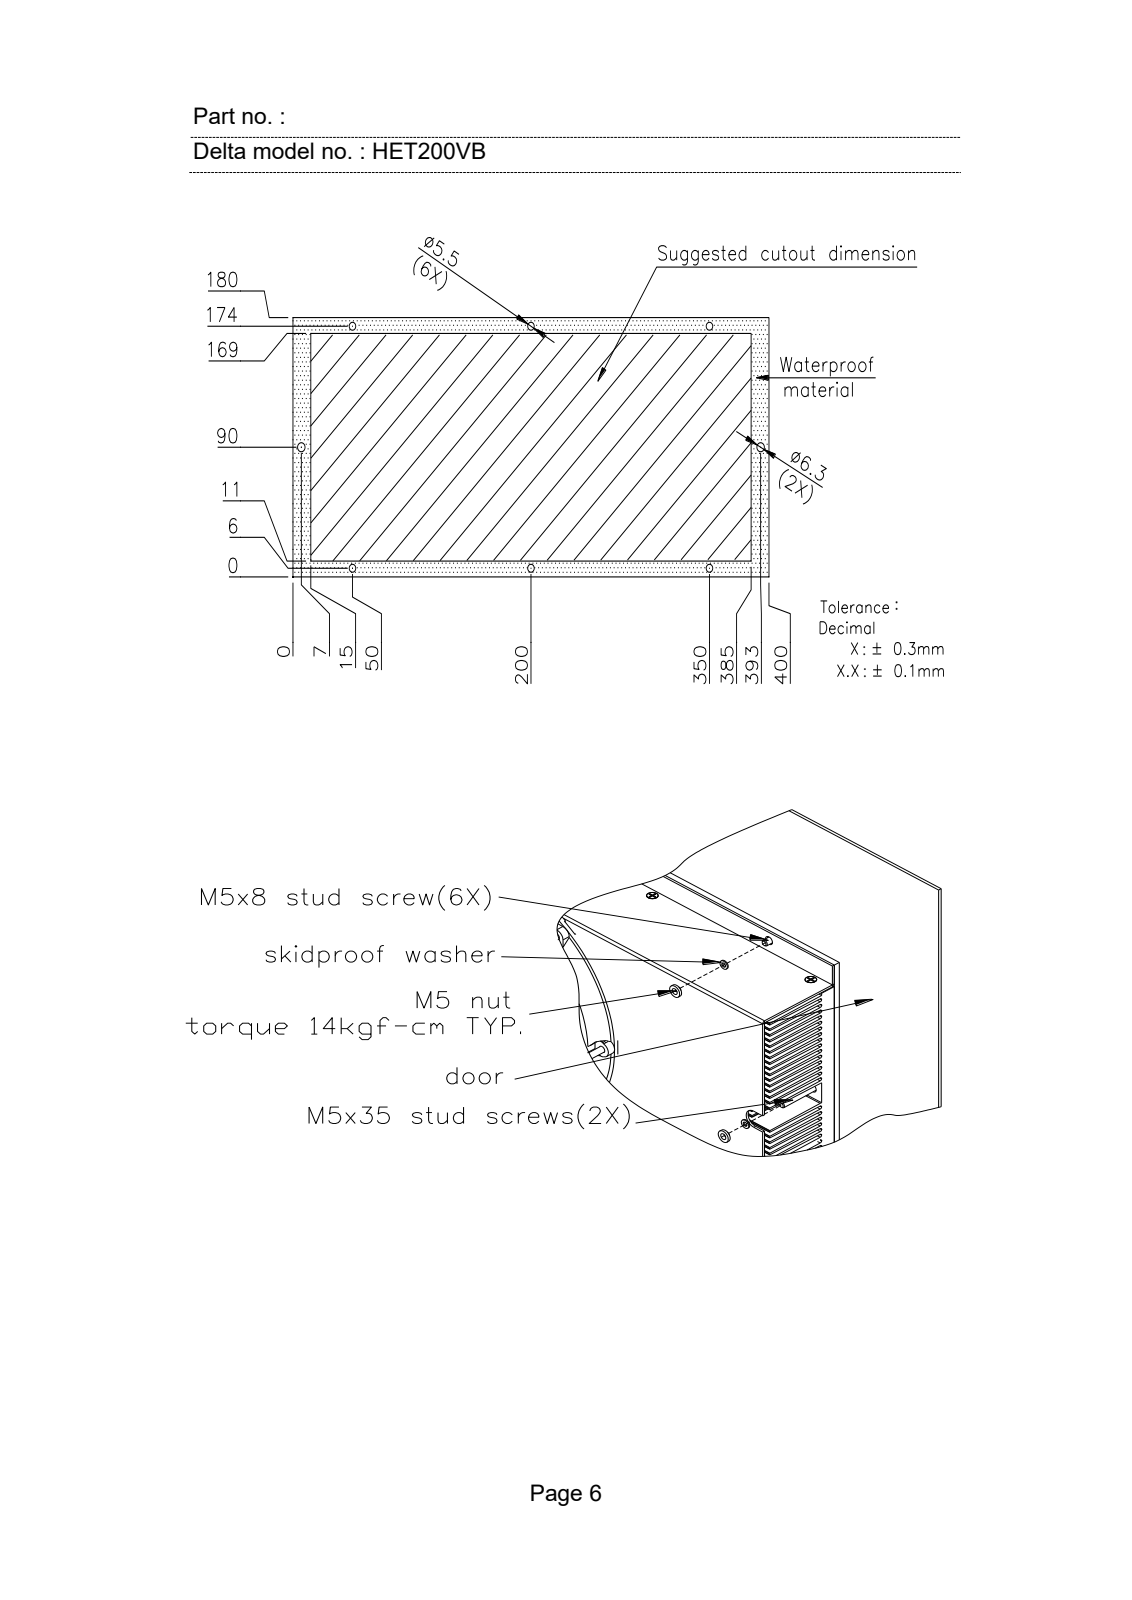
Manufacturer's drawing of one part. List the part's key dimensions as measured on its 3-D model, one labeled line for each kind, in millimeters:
Part name (STEP PRODUCT): HET200PB_MODULE_ALL_01
STEP written by: CREO PARAMETRIC BY PTC INC, 2015290 (CONFIG_CONTROL_DESIGN)
Units: millimetres
Bodies: 1 solid, 294 faces (139 planar, 120 cylindrical, 35 other)
Overall size (bounding box): 400 × 209.72 × 180
Volume: 2 420 000 mm³ · Surface area: 609 263 mm²
Round holes (diameter × count): ⌀4 ×13, ⌀5.5 ×6, ⌀3 ×4, ⌀3.5 ×4, ⌀4.5 ×4
Partial cylindrical surfaces — rounded edges, fillets, slot ends (radius × count): R1.5 ×12, R2 ×10, R5 ×4, R4.5 ×2, R4.5 ×2, R6 ×2, R8.5 ×2, R10 ×2
Main face-to-face distances: 1.5, 54, 108, 150.5, 55.5, 4, 59.5, 52.5, 109.5, 50
Hole centre spacings: 10.01, 59.74, 61.22, 72, 102.46, 105, 108.71, 115.93
